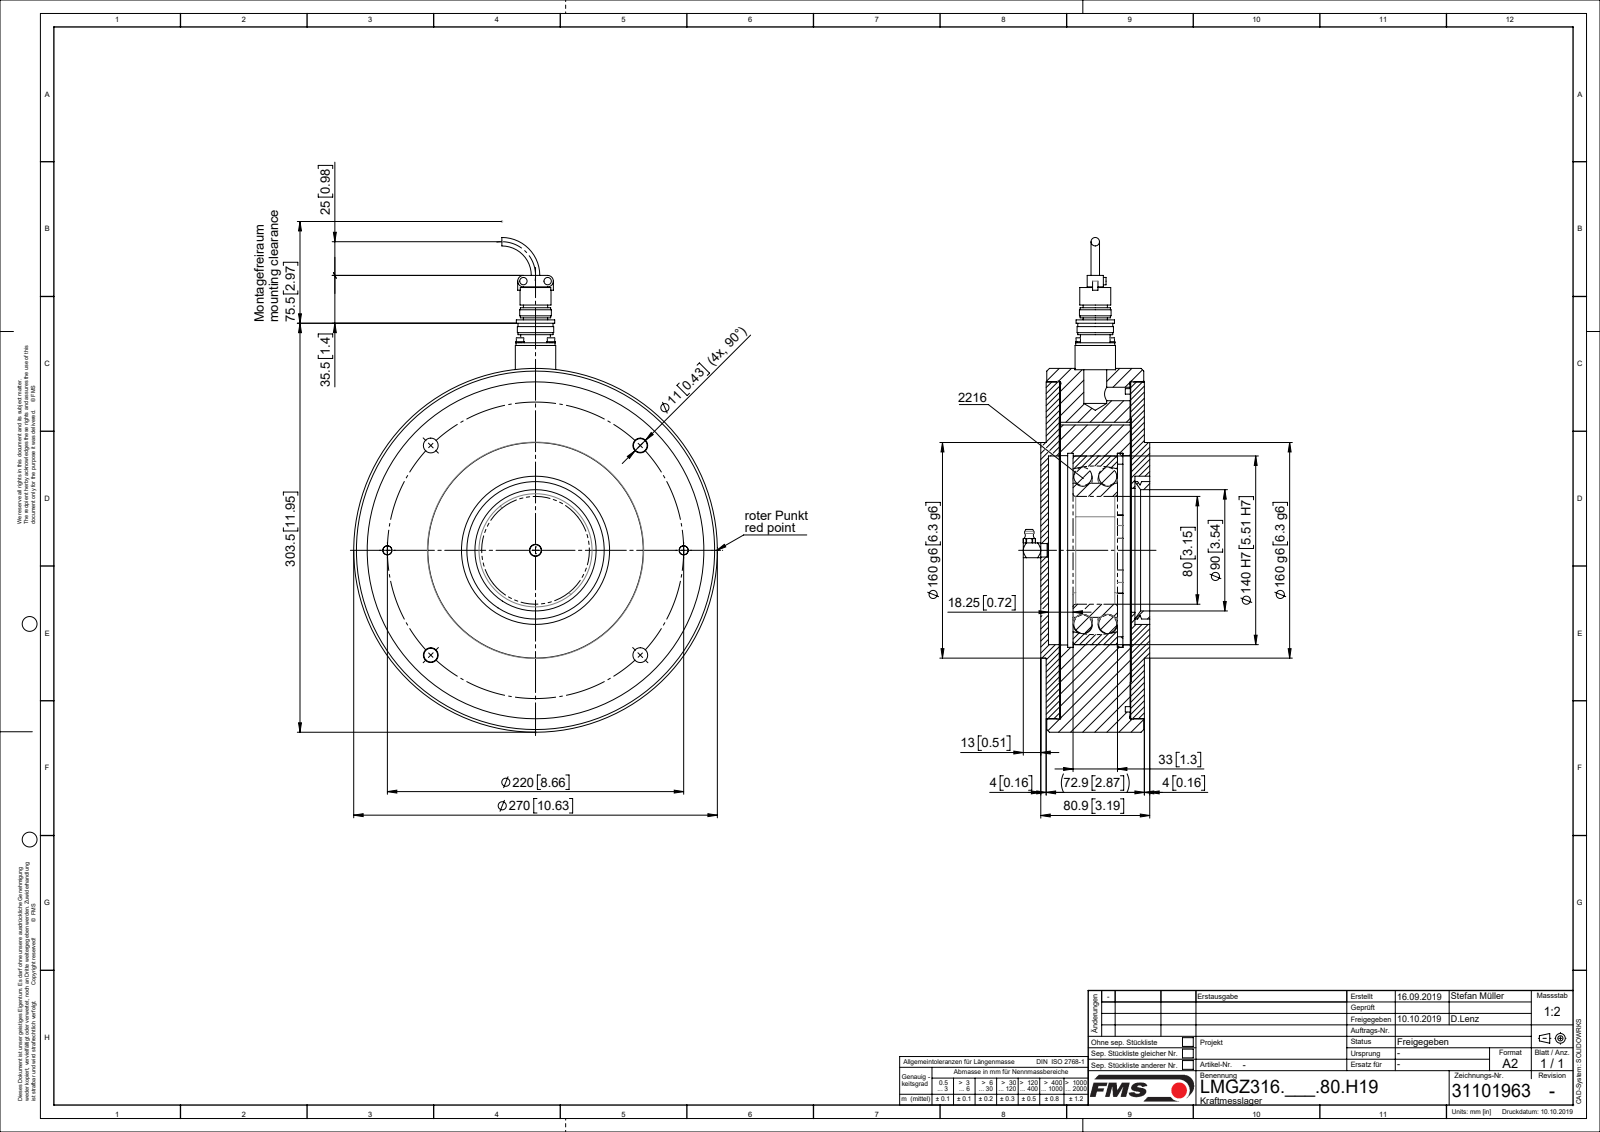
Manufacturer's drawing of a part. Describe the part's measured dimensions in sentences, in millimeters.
The part is named "ZEICHNUNG2; L50045; L4899004; TEIL1 (+8 more)". Its 3-D file was written by "Mechanical Desktop 2009 (CONFIG_CONTROL_DESIGN)". It is 21 solids with 408 faces: 112 planar, 230 cylindrical and 66 other. Overall it measures 367.15 by 335 by 270 millimeters. Its volume is 3 608 000 cubic millimeters and its surface area 571 523 square millimeters. Round holes: 4 of diameter 2.6, 4 of diameter 3.2, 4 of diameter 3.4, 4 of diameter 11, 4 of diameter 12, 3 of diameter 9, 2 of diameter 6.91, 2 of diameter 10, 2 of diameter 10.2, 2 of diameter 15, 1 of diameter 23, 1 of diameter 80. Round bosses or shafts: 6 of diameter 5.5, 4 of diameter 6.2, 4 of diameter 3, 4 of diameter 2.5, 3 of diameter 8, 2 of diameter 13, 1 of diameter 270, 1 of diameter 250. Partial cylindrical surfaces (rounded edges, fillets, slot ends): 2 of radius 4.25. The main face-to-face distances are 52.3, 62.8, 10.5, 10.2, 62.5, 52, 0.5, 9.7, 4, 0.8. The hole center spacings are 110, 16.26, 23, 84.19, 155.56, 203.25, 220, 32.53.
